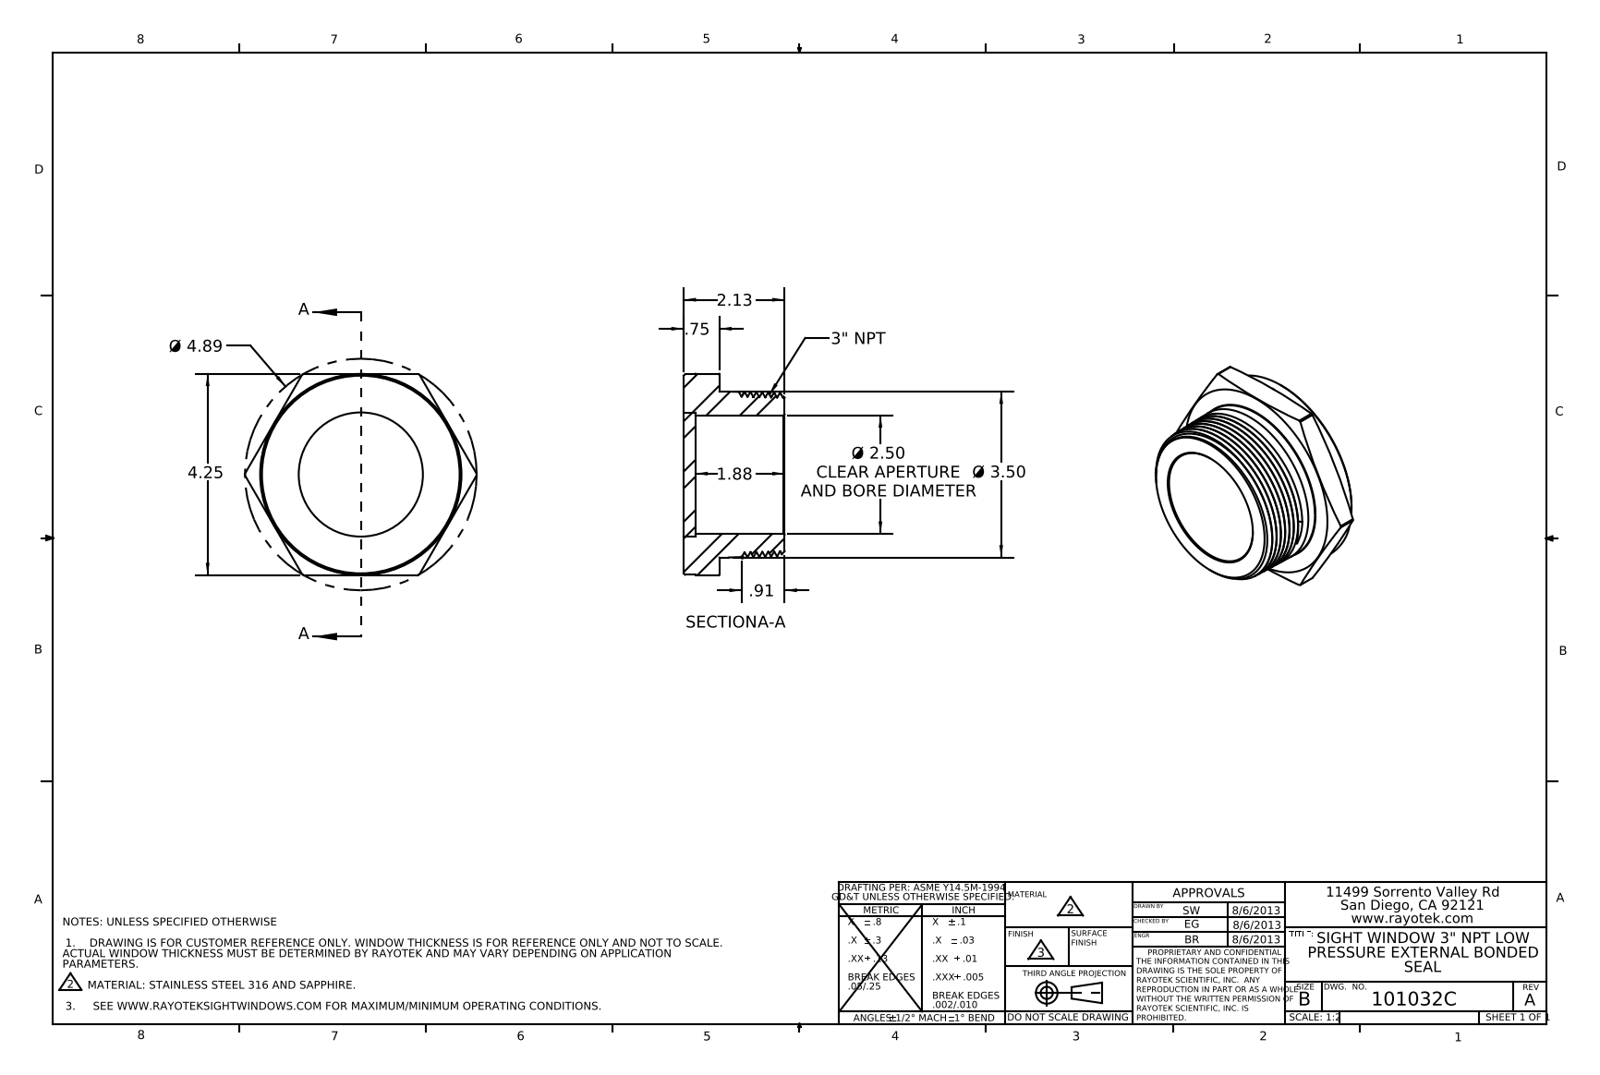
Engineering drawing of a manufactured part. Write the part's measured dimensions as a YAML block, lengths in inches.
part_name: "403032"
step_written_by: "SolidWorks 2012 (AUTOMOTIVE_DESIGN)"
units: inches
bodies: {solids: 2, faces: 65, planar: 15, cylindrical: 17, other: 33}
overall_size: [4.887, 4.25, 2.13]
volume: 14.59
surface_area: 82.84
round_holes:
  - {diameter: 2.5, count: 1}
  - {diameter: 2.62, count: 1}
round_bosses_or_shafts:
  - {diameter: 4.23, count: 1}
  - {diameter: 3.5, count: 1}
partial_cylinders:
  - {radius: 2.444, count: 1}
face_to_face_distances: [0.246, 0.75, 0.504, 4.25, 2.13, 1.884, 1.38]
